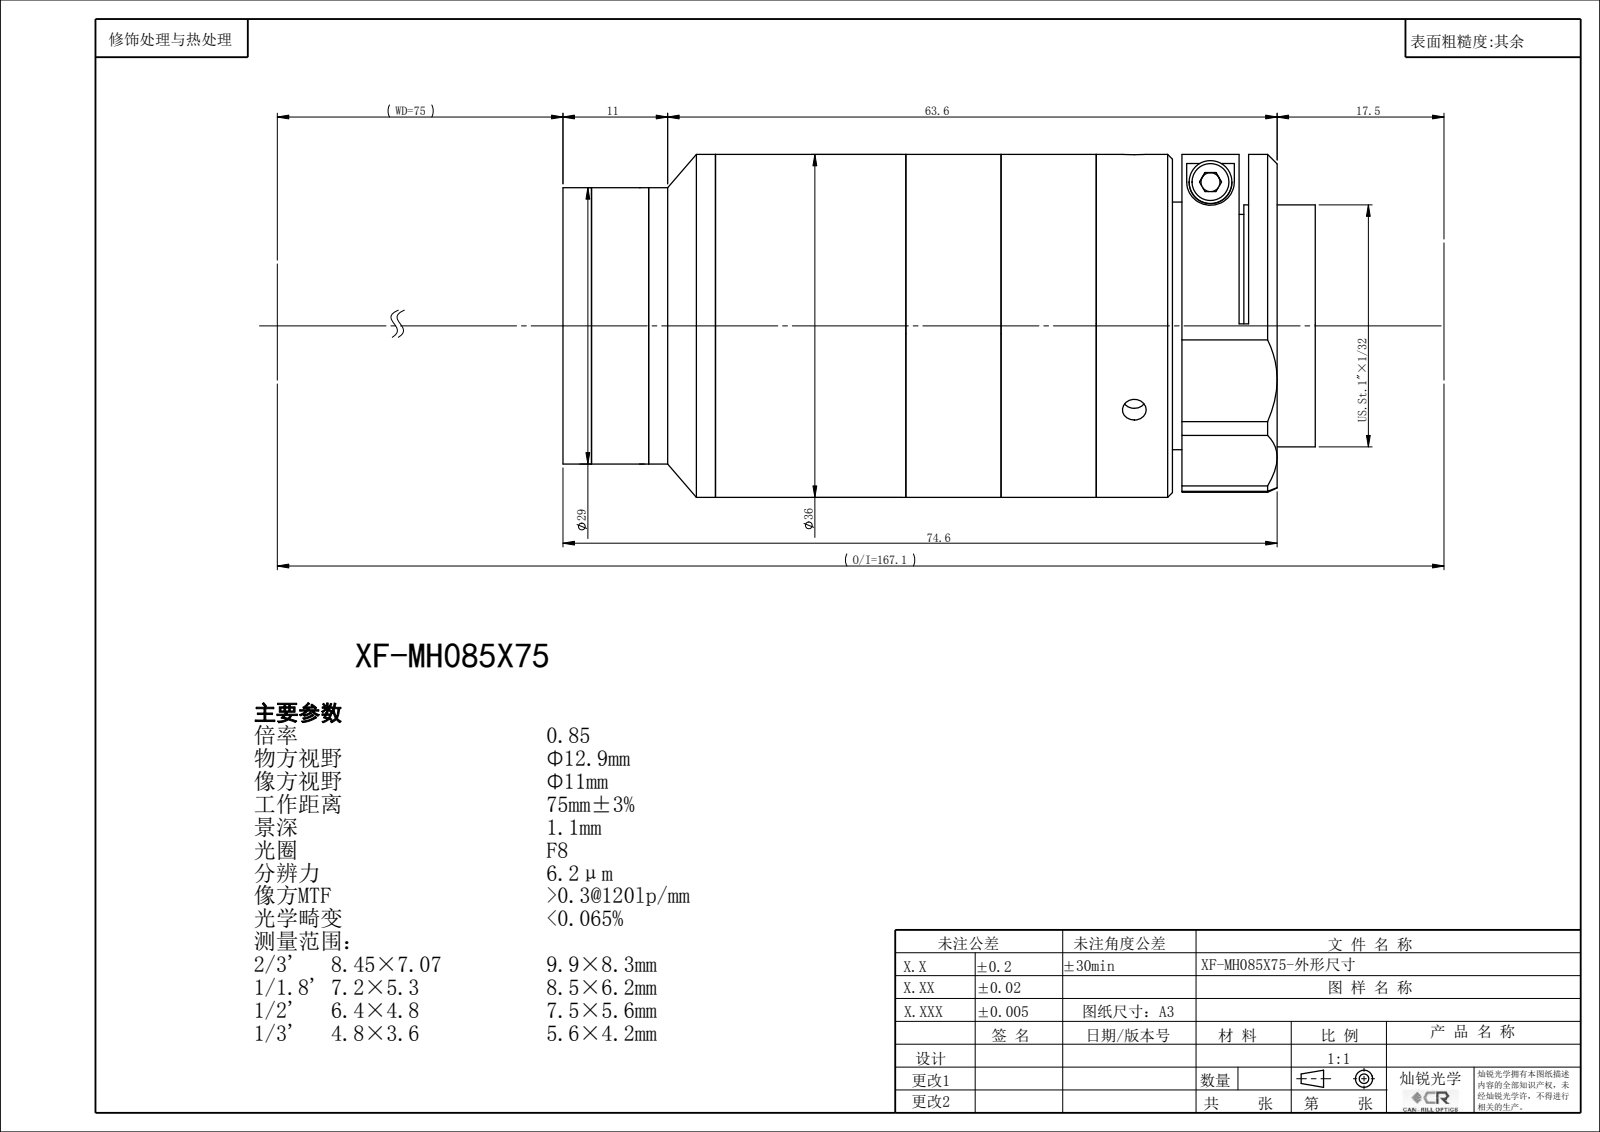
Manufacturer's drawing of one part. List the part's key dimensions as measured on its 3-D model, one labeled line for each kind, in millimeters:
Part name (STEP PRODUCT): XF-MH085X75
STEP written by: SolidWorks 2022 (CONFIG_CONTROL_DESIGN)
Units: millimetres
Bodies: 0 solids, 129 faces (65 planar, 42 cylindrical, 22 other)
Overall size (bounding box): 78.76 × 36.01 × 36
Round holes (diameter × count): ⌀2.5 ×3, ⌀14 ×1, ⌀22.4 ×1, ⌀24 ×1, ⌀24.9 ×1, ⌀27 ×1
Round bosses / shafts (diameter × count): ⌀36 ×1, ⌀34 ×1, ⌀29 ×1, ⌀25.4 ×1
Main face-to-face distances: 10, 20, 18.74, 52.22, 70.96, 1.5, 69.46, 17.24, 42.22, 27.24
